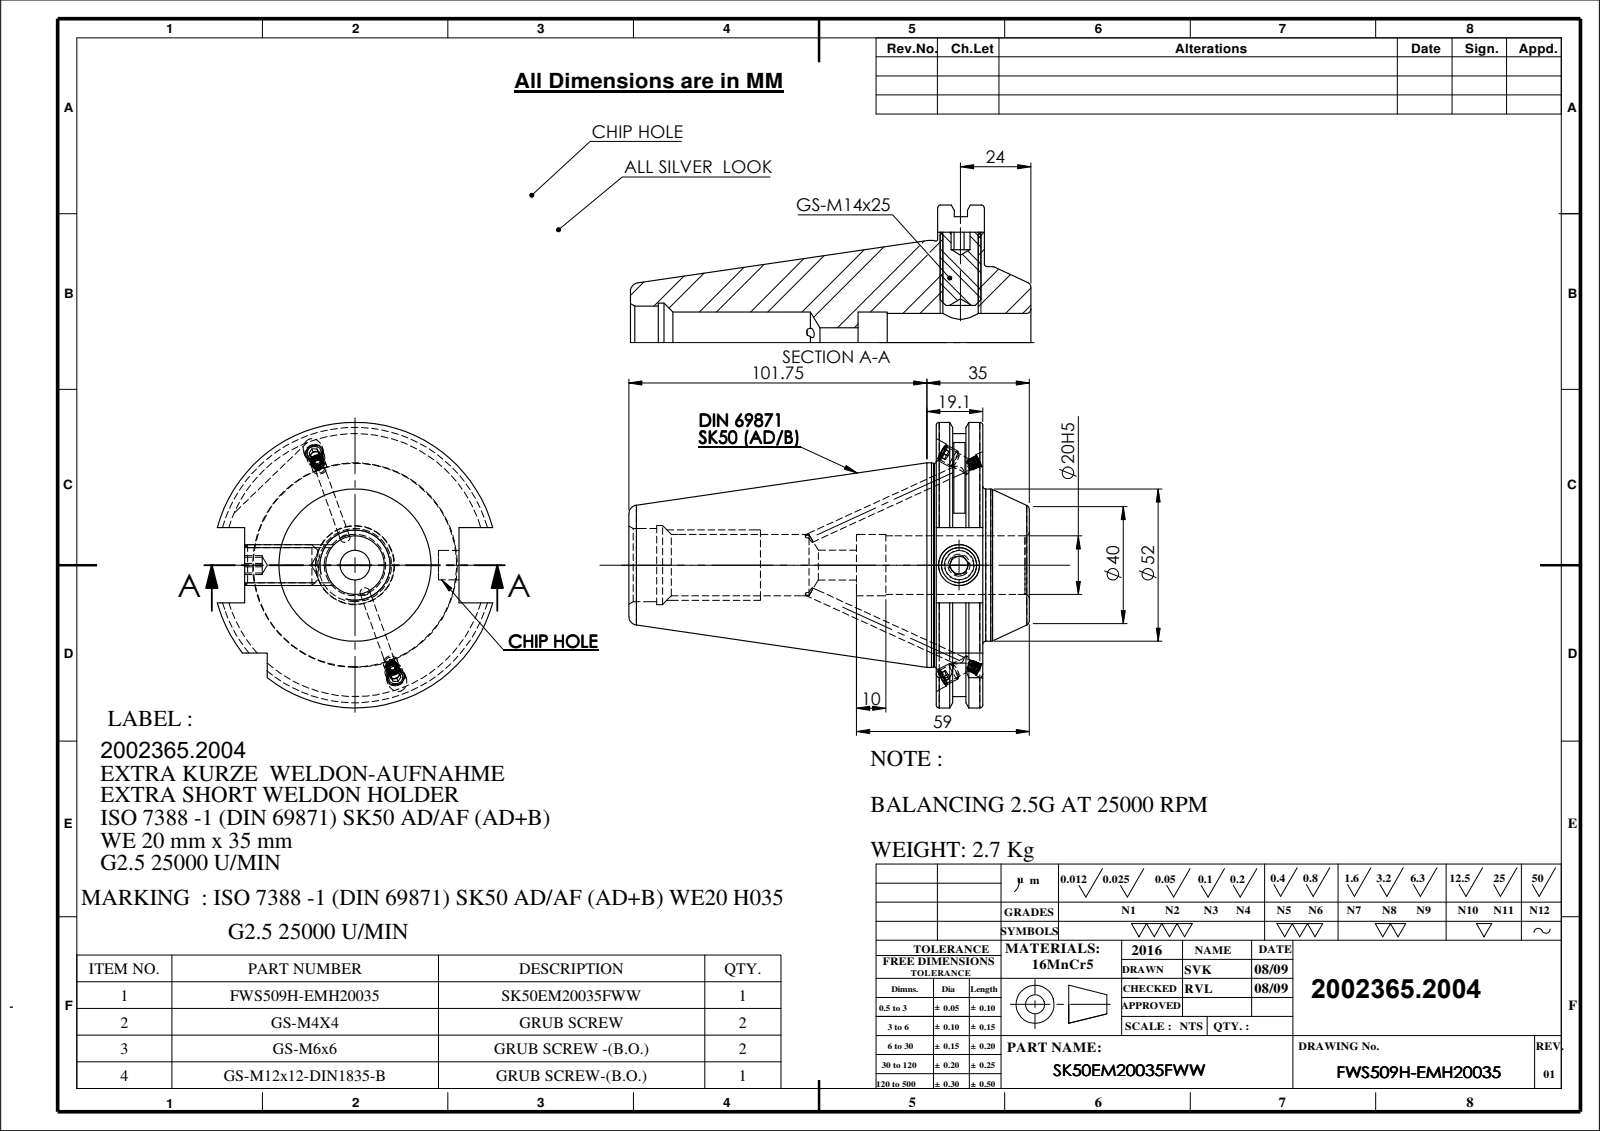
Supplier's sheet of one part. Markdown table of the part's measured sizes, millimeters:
| quantity | value |
| --- | --- |
| part name | SK50EM20035FWW; GS-M4X4_DIN 913 - M4 x 4-N; M6X6_DIN 913 - M6 x 6-N; GS-M14X25 (+1 more) |
| STEP written by | SolidWorks 2018 (CONFIG_CONTROL_DESIGN) |
| units | millimeters |
| bodies | 6 solids, 279 faces (81 planar, 80 cylindrical, 118 other) |
| overall size | 136.75 × 97.5 × 94.05 |
| volume | 345 816 mm³ |
| surface area | 50 772 mm² |
| round holes (diameter × count) | 3.3 × 2, 4.5 × 2, 5 × 2, 6.5 × 2, 10 × 1, 10.2 × 1, 12 × 1, 20 × 1, 21 × 1, 25 × 1, 27 × 1 |
| round bosses / shafts (diameter × count) | 6 × 2, 4 × 2, 89.8 × 1, 69.85 × 1, 69.45 × 1, 52 × 1, 14 × 1 |
| partial cylindrical surfaces (radius × count) | 48.75 × 1 |
| main face-to-face distances | 15.9, 31.8, 10.14, 5.76, 21.66, 5.66, 4.48, 10.24, 26.14, 104.95 |
